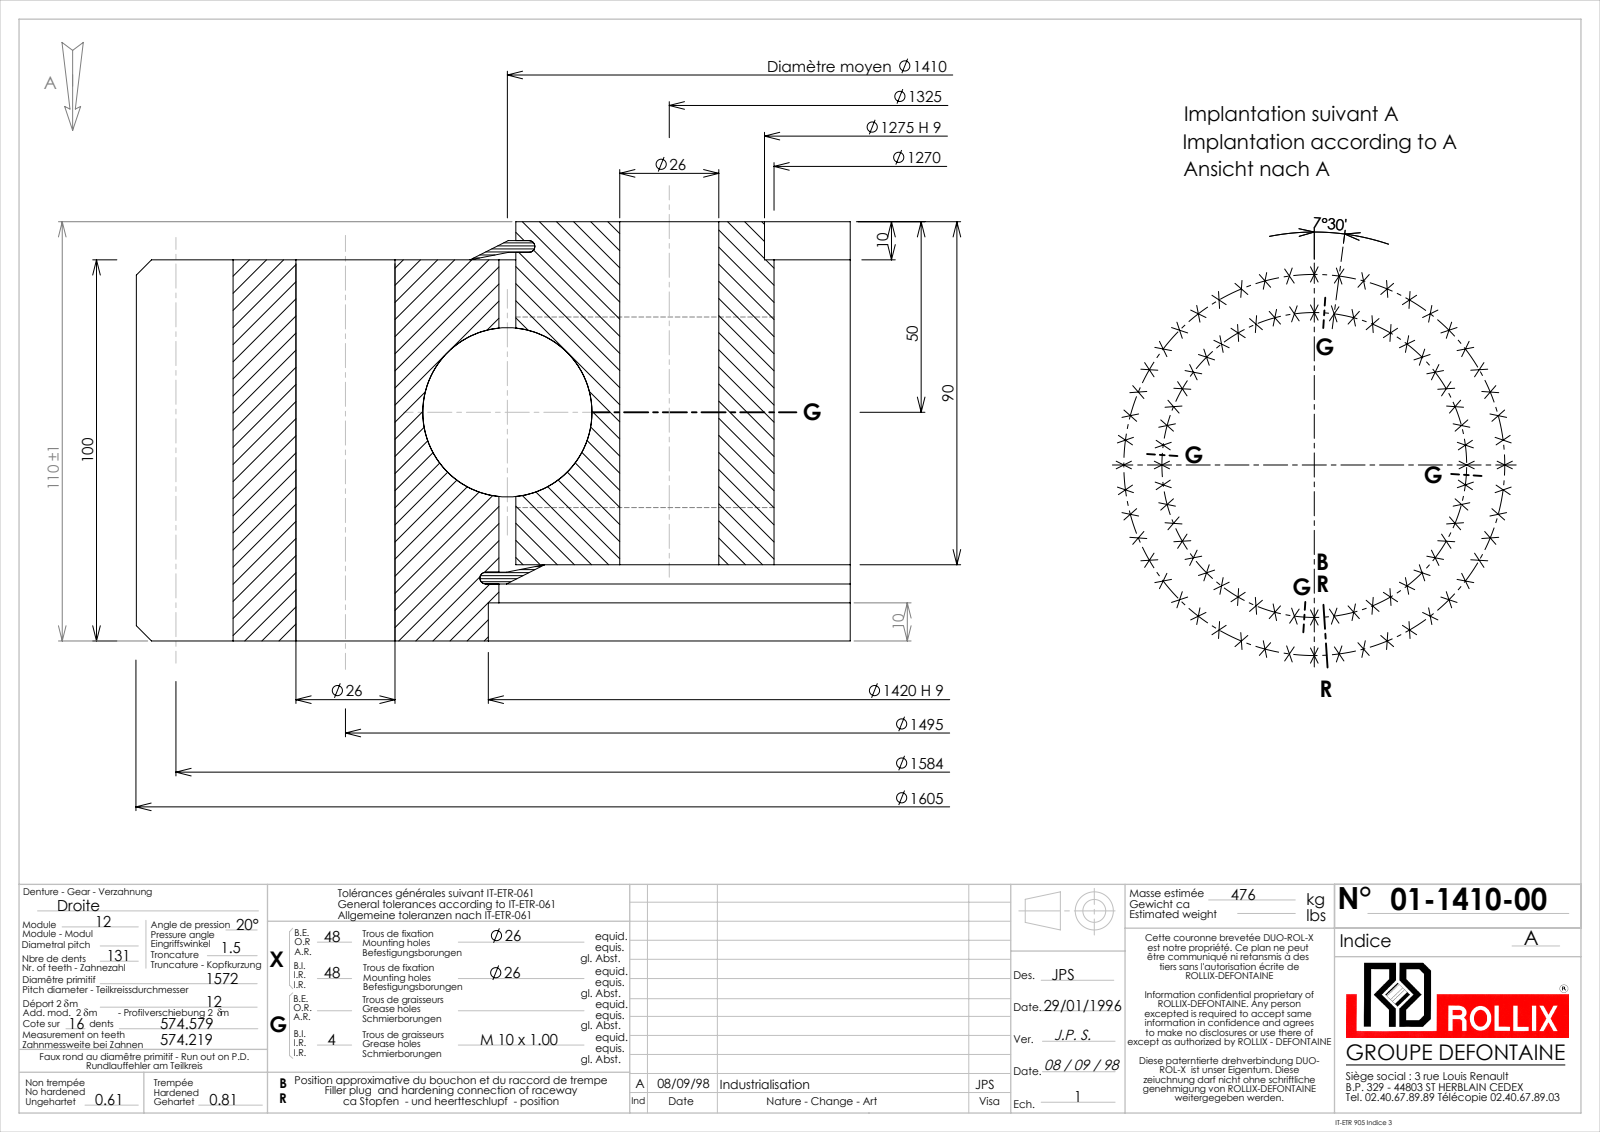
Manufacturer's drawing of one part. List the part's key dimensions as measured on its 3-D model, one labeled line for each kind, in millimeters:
Part name (STEP PRODUCT): 01-1410-00
STEP written by: SolidWorks 2016 (CONFIG_CONTROL_DESIGN)
Units: millimetres
Bodies: 5 solids, 1048 faces (276 planar, 481 cylindrical, 291 other)
Overall size (bounding box): 1604.98 × 1604.89 × 110
Volume: 54 160 000 mm³ · Surface area: 4 765 000 mm²
Round holes (diameter × count): ⌀26 ×96, ⌀9 ×4, ⌀1270 ×1, ⌀1275 ×1, ⌀1414.44 ×1, ⌀1420 ×1
Round bosses / shafts (diameter × count): ⌀1405.56 ×1
Partial cylindrical surfaces — rounded edges, fillets, slot ends (radius × count): R777 ×1, R802.5 ×1
Main face-to-face distances: 100, 10, 90, 20, 80, 110, 5.05, 85.05, 3.1, 1.95
Hole centre spacings: 97.78, 291.66, 830.58, 910.1, 985.72, 747.5, 480.55, 195.14
